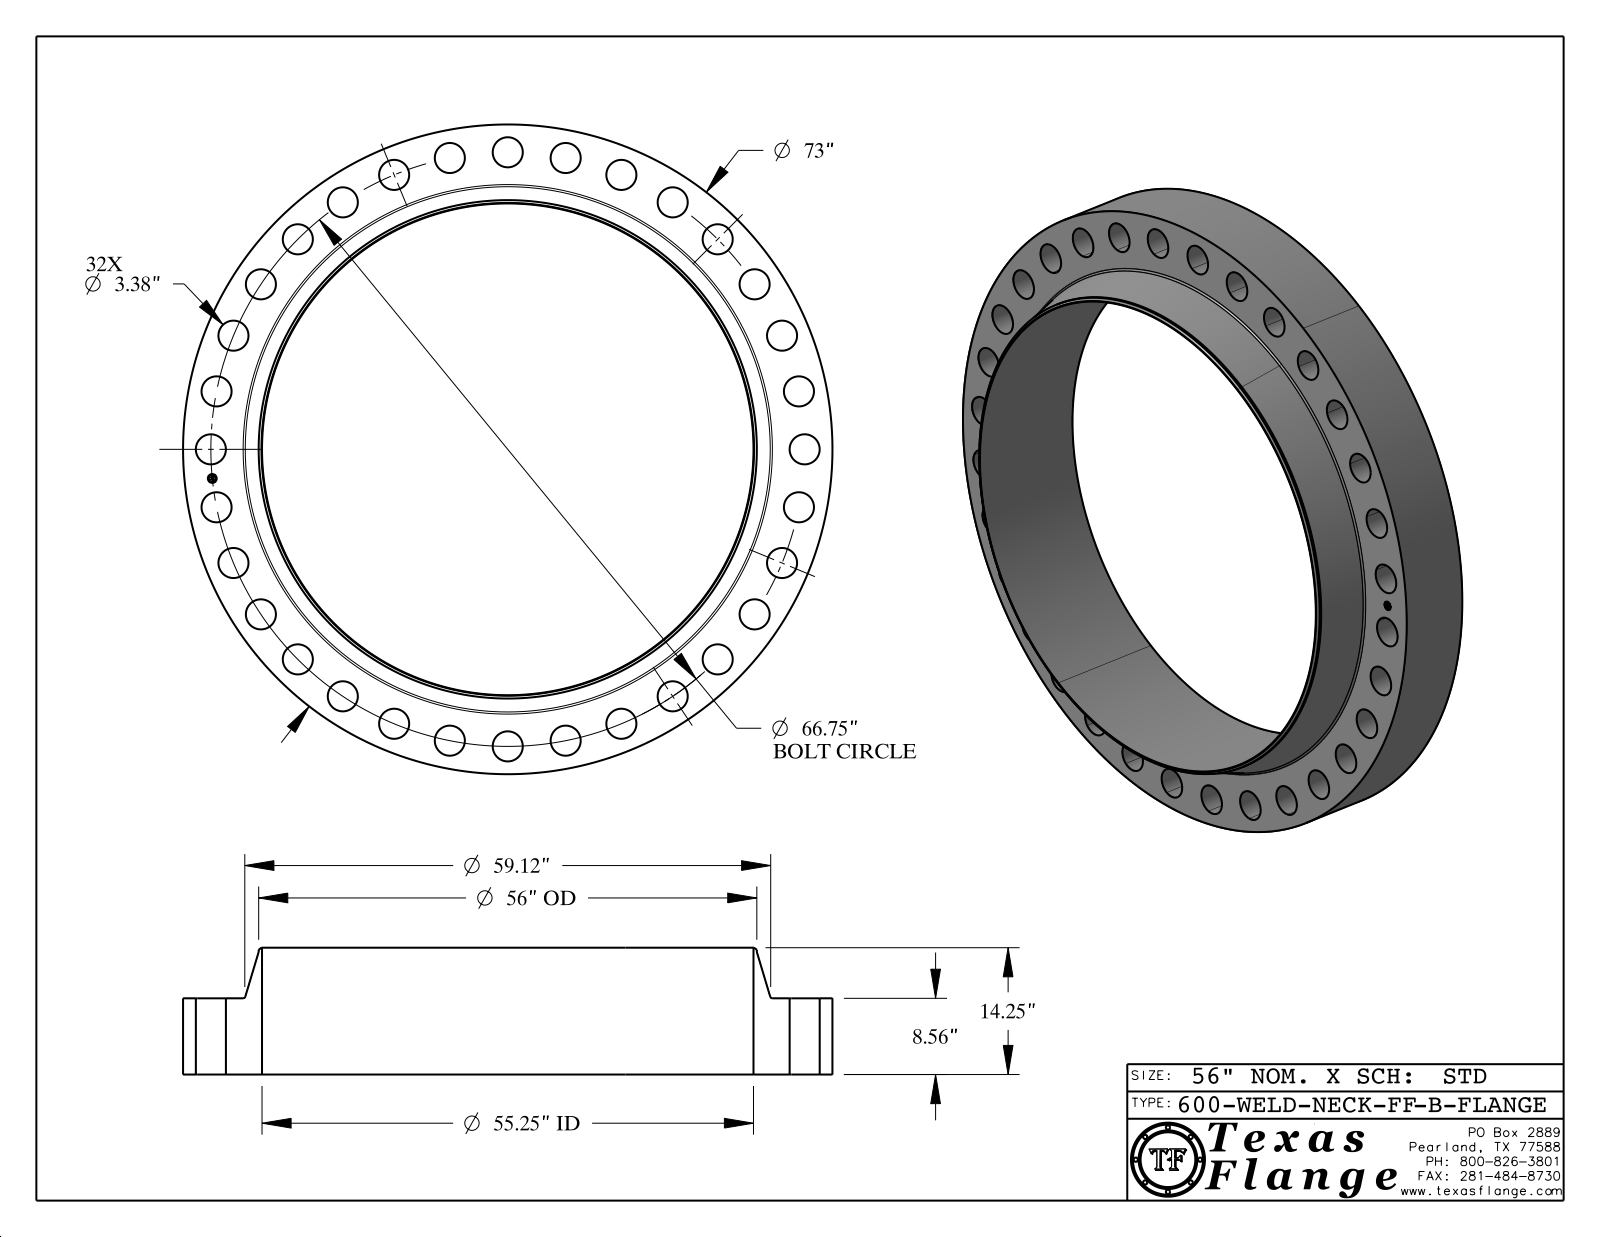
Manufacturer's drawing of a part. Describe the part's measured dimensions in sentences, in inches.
The part is named "600-WELD-NECK-FF, Series B". Its 3-D file was written by "CATIA V5 STEP AP214 (AUTOMOTIVE_DESIGN)". It is 1 solid with 464 faces: 368 planar, 90 cylindrical and 6 other. Overall it measures 73 by 73 by 14.25 inches. Its volume is 13 943 cubic inches and its surface area 11 095 square inches. Round holes: 32 of diameter 3.38, 1 of diameter 1, 1 of diameter 55.25. Round bosses or shafts: 8 of diameter 0.061, 1 of diameter 73, 1 of diameter 56, 1 of diameter 0.788. The main face-to-face distances are 8.56, 14.25, 5.69, 0.015, 8.545, 5.705, 0.298, 0.292, 0.054, 0.193. The hole center spacings are 55.501, 58.869, 33.375, 13.022, 47.2, 31.466, 51.598, 63.876.
